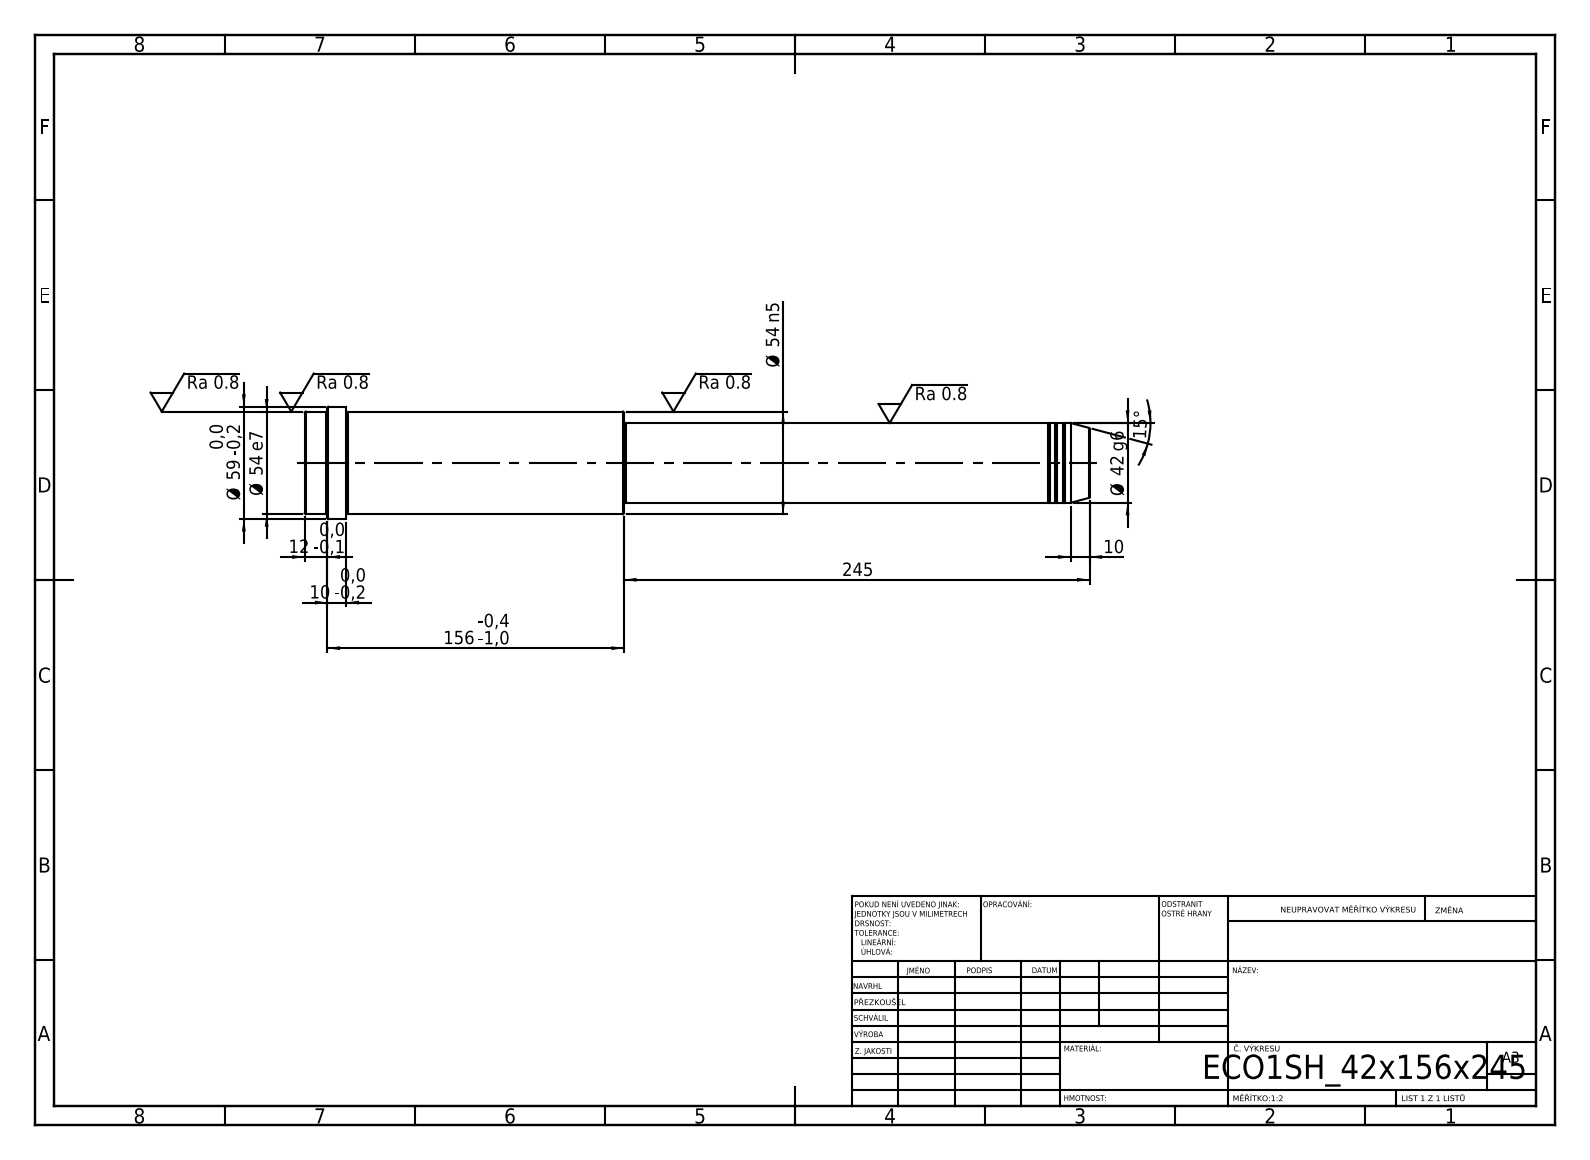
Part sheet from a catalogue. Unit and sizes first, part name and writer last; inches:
Units: inches
Overall size (bounding box): 16.26 × 2.323 × 2.323
Round bosses / shafts (diameter × count): ⌀2.323 ×1, ⌀2.126 ×1, ⌀1.654 ×1, ⌀1.614 ×1
Main face-to-face distances: 16.26, 9.646, 6.614, 15.394, 5.748, 0.866, 15.787, 6.142, 0.394, 0.472
Volume: 44.33 in³ · Surface area: 103 in²
Bodies: 1 solid, 52 faces (6 planar, 16 cylindrical, 30 other)
STEP written by: SolidWorks 2019 (CONFIG_CONTROL_DESIGN)
